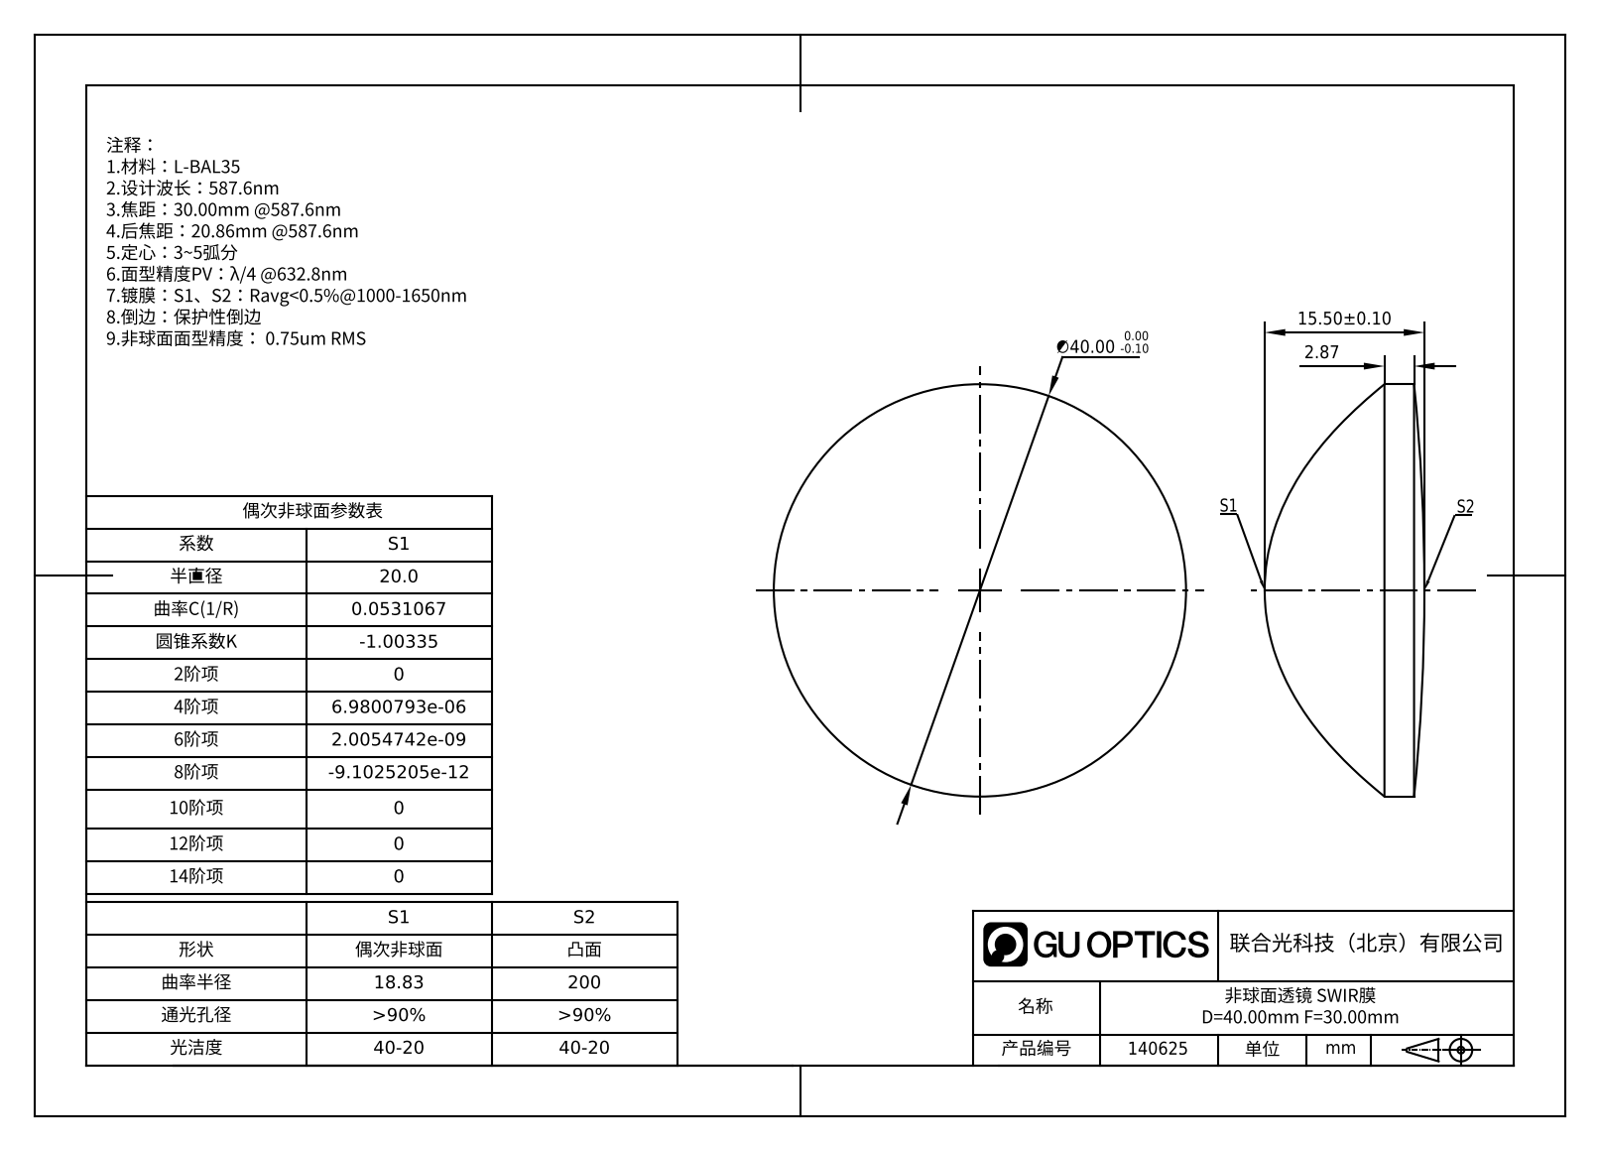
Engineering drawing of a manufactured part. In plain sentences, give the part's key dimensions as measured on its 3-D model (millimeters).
The part is named "140610". Its 3-D file was written by "SolidWorks 2020 (CONFIG_CONTROL_DESIGN)". It is 1 solid with 5 faces: 0 planar, 2 cylindrical and 3 other. Overall it measures 40 by 40 by 15.5 millimeters. Its volume is 11 732 cubic millimeters and its surface area 3 250 square millimeters. Round bosses or shafts: 1 of diameter 40.
